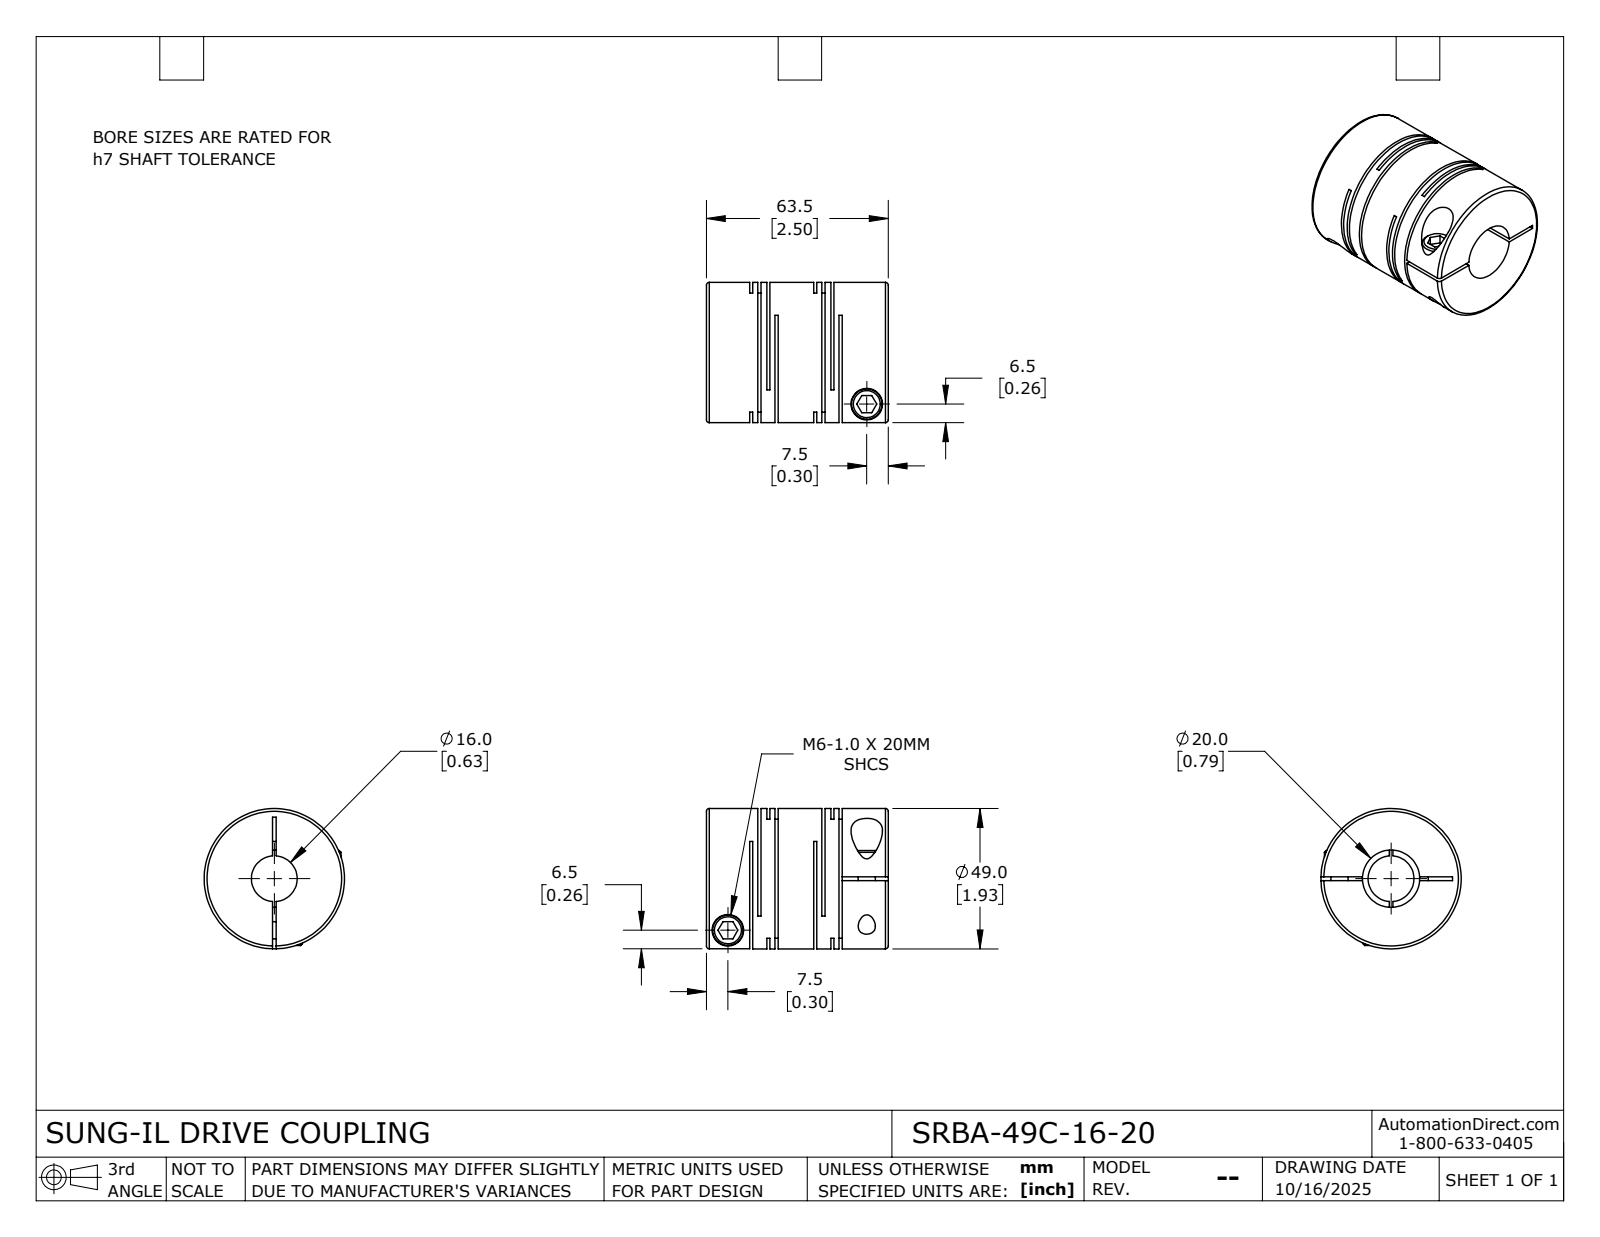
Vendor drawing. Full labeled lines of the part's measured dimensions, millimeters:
Part name (STEP PRODUCT): SRBA-49C-16-20
STEP written by: SolidWorks 2024 (CONFIG_CONTROL_DESIGN)
Units: millimetres
Bodies: 1 solid, 115 faces (60 planar, 42 cylindrical, 13 other)
Overall size (bounding box): 63.5 × 49 × 49
Volume: 87 839 mm³ · Surface area: 38 122 mm²
Round holes (diameter × count): ⌀6 ×2, ⌀11 ×2, ⌀16 ×1, ⌀20 ×1
Round bosses / shafts (diameter × count): ⌀10.6 ×2, ⌀49 ×1
Main face-to-face distances: 6, 1.1, 22.35, 2.85, 21.25, 3.15, 1.75, 4.9, 19.5, 16.35
